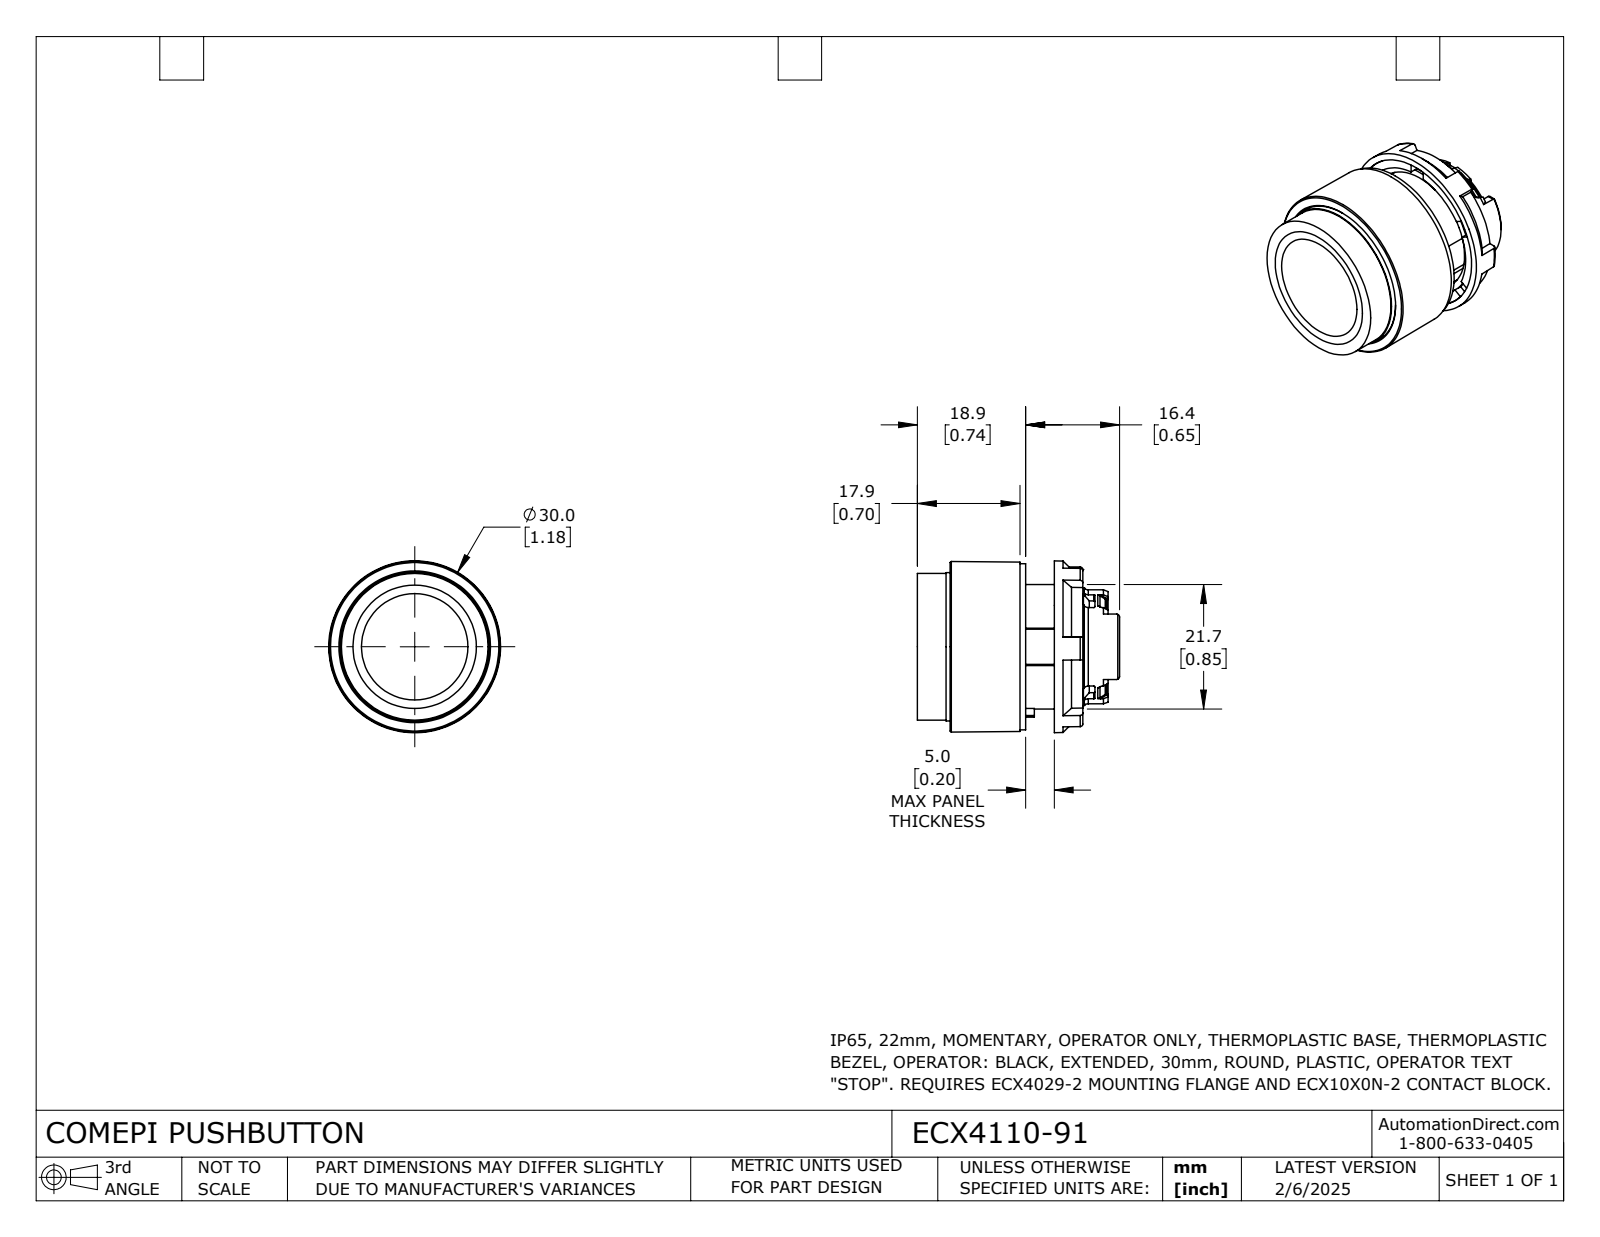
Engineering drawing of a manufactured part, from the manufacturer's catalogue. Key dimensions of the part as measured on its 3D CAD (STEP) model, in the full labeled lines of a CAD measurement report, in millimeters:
Part name (STEP PRODUCT): ECX4110-91
STEP written by: SolidWorks 2024 (CONFIG_CONTROL_DESIGN)
Units: millimetres
Bodies: 3 solids, 401 faces (135 planar, 113 cylindrical, 153 other)
Overall size (bounding box): 35.3 × 30 × 30
Volume: 10 800 mm³ · Surface area: 11 140 mm²
Round holes (diameter × count): ⌀13.5 ×1, ⌀18.1 ×1, ⌀22.1 ×1
Round bosses / shafts (diameter × count): ⌀29 ×1, ⌀25.9 ×1, ⌀25.6 ×1, ⌀24.5 ×1, ⌀21.7 ×1, ⌀20.5 ×1, ⌀20 ×1, ⌀19 ×1
Partial cylindrical surfaces — rounded edges, fillets, slot ends (radius × count): R0.2 ×24, R0.5 ×8, R0.3 ×2, R7.4 ×1, R8.7 ×1, R8.8 ×1, R9.3 ×1
Main face-to-face distances: 10.4, 1, 11, 6, 5, 11.4, 5.5, 5.9, 15.5, 4.5
